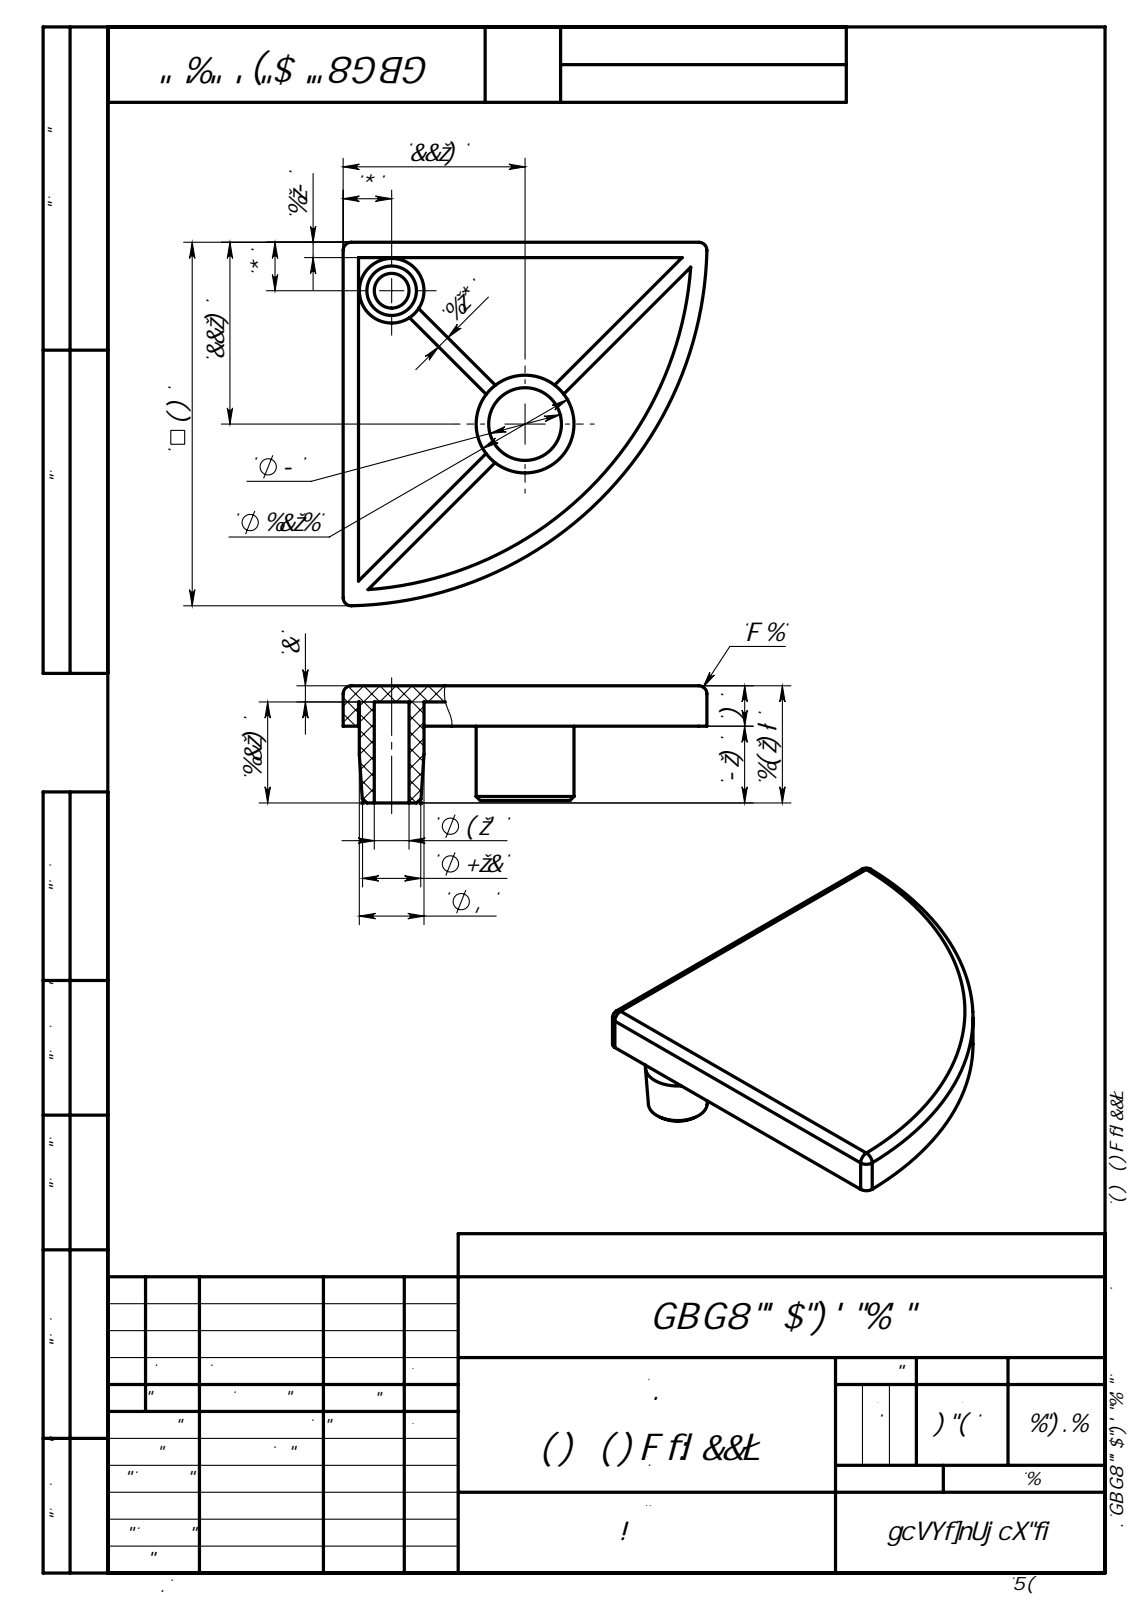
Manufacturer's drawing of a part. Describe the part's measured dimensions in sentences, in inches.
The part is named "Сборка2". Its 3-D file was written by "SolidWorks 2014 (AUTOMOTIVE_DESIGN)". It is 1 solid with 44 faces: 19 planar, 15 cylindrical and 10 other. Overall it measures 1.771 by 1.771 by 0.571 inches. Its volume is 0.296 cubic inches and its surface area 9.241 square inches. Round holes: 1 of diameter 0.169, 1 of diameter 0.354. Round bosses or shafts: 1 of diameter 0.476, 1 of diameter 0.315. Partial cylindrical surfaces (rounded edges, fillets, slot ends): 5 of radius 0.039, 1 of radius 1.74, 1 of radius 1.772. The main face-to-face distances are 0.079, 0.031, 0.118, 0.197, 0.063, 0.362, 0.48, 0.559, 0.374, 0.492. The hole center spacings are 0.919.
